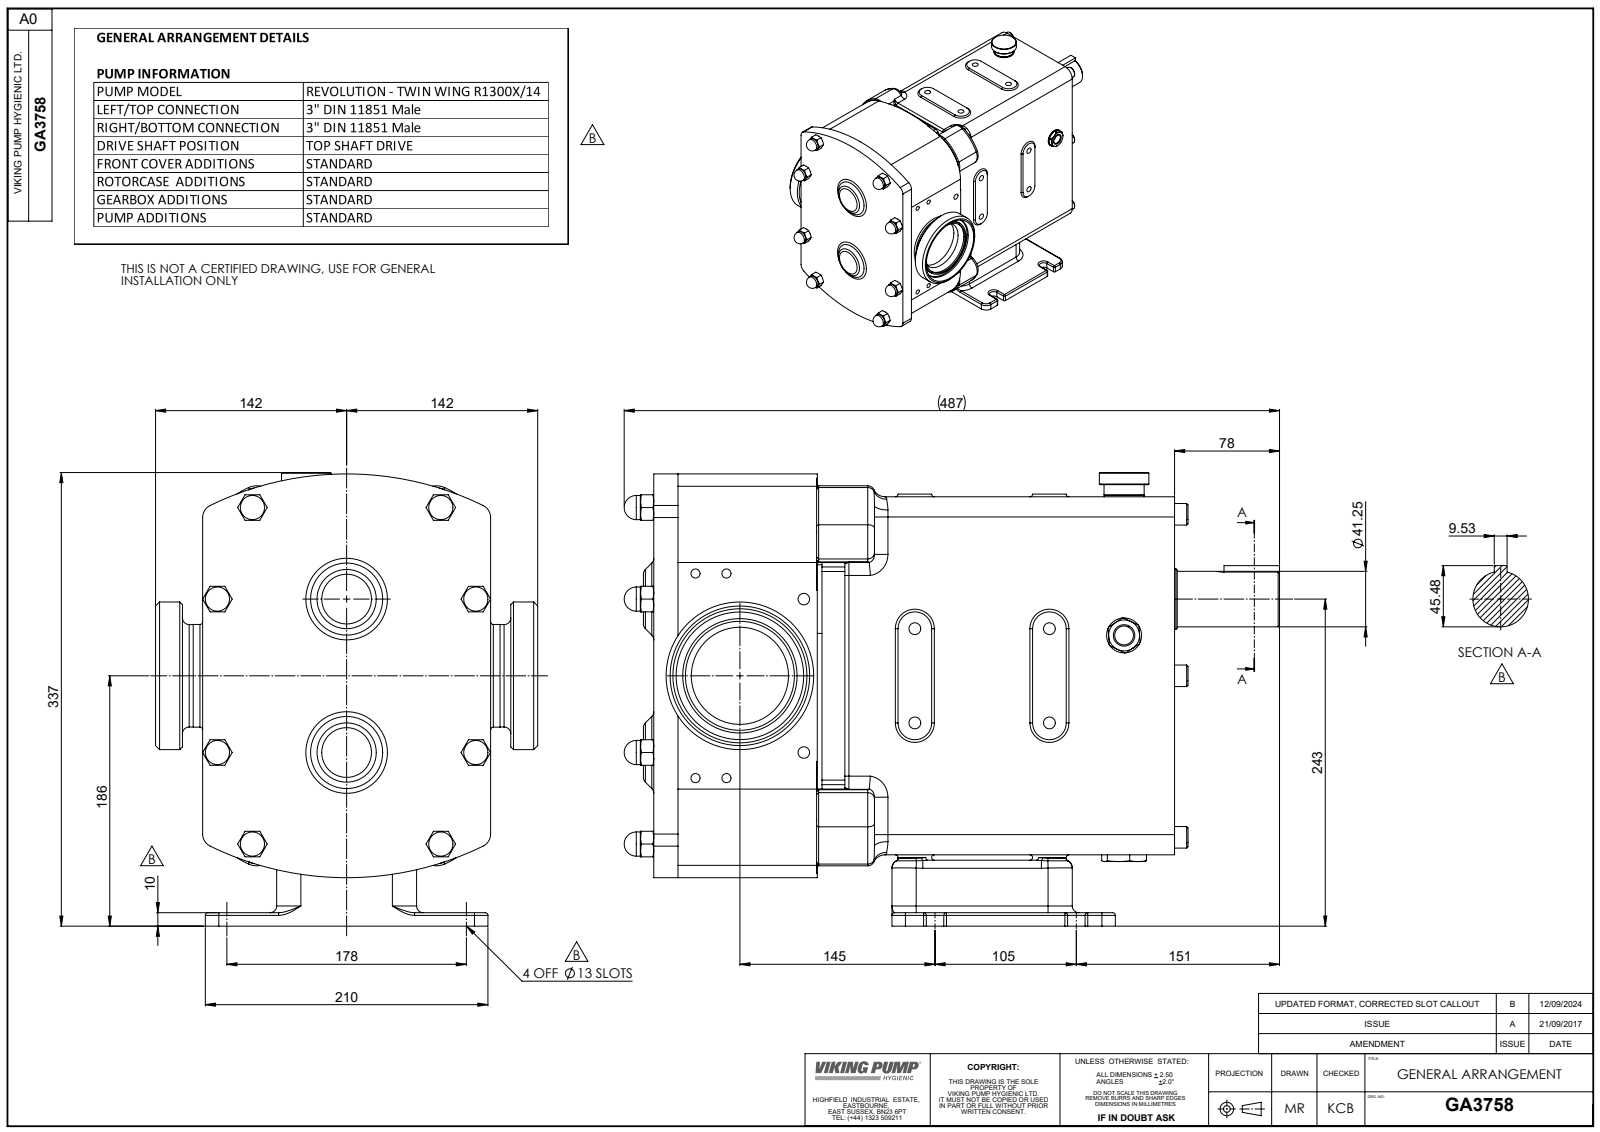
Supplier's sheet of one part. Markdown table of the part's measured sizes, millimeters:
| quantity | value |
| --- | --- |
| part name | Copy of Z94-5031-55 - 3 INCH DIN11851^GA3758; GA3758; Copy of R1300 CPP H TSD^GA3758 |
| STEP written by | SolidWorks 2023 (AUTOMOTIVE_DESIGN) |
| units | millimeters |
| bodies | 3 solids, 960 faces (303 planar, 296 cylindrical, 361 other) |
| overall size | 487 × 337 × 284 |
| volume | 18 770 000 mm³ |
| surface area | 732 434 mm² |
| round holes (diameter × count) | 8.8 × 8, 6.8 × 4, 8.6 × 2, 14 × 1, 33.8 × 1, 72.2 × 1, 81 × 1, 94.8 × 1 |
| round bosses / shafts (diameter × count) | 18 × 8, 16 × 6, 109.7 × 1, 85 × 1, 76.3 × 1, 76.1 × 1, 51 × 1, 45 × 1 |
| partial cylindrical surfaces (radius × count) | 2 × 38, 10 × 30, 5 × 19, 5.9 × 8, 15 × 8, 18 × 8, 3 × 4, 6 × 4 |
| main face-to-face distances | 152, 121.5, 265.5, 387, 183, 31, 125, 3.5, 262, 43 |
| hole center spacings | 70, 100, 122.07, 23, 55.72, 60.56, 74.2, 76.66 |
